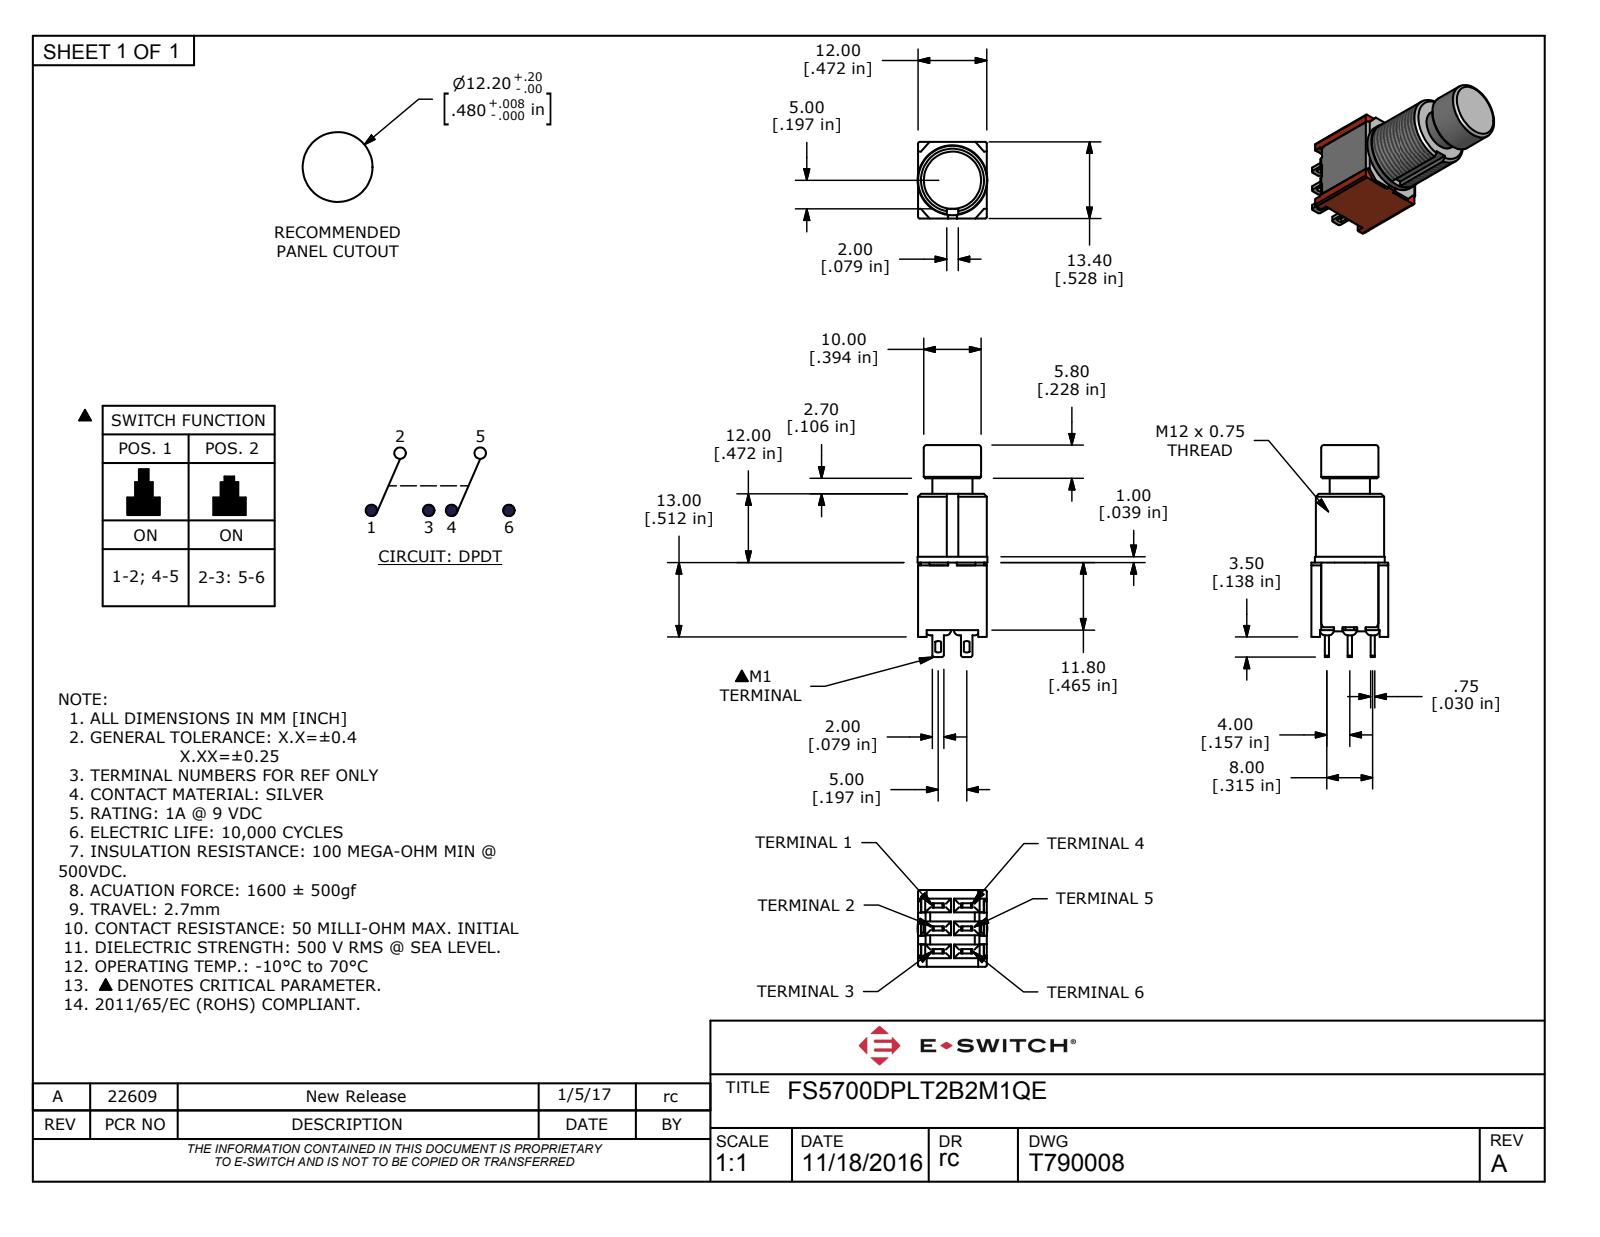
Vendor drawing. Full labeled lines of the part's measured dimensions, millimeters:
Part name (STEP PRODUCT): FS5700DPLT2B2M1QE
STEP written by: Autodesk Inventor 2022 (AUTOMOTIVE_DESIGN)
Units: millimetres
Bodies: 1 solid, 344 faces (258 planar, 83 cylindrical, 3 other)
Overall size (bounding box): 37 × 13.4 × 12.2
Volume: 2 139 mm³ · Surface area: 3 376 mm²
Round holes (diameter × count): ⌀9 ×1
Round bosses / shafts (diameter × count): ⌀12.2 ×1, ⌀12 ×1, ⌀10 ×1, ⌀7 ×1
Partial cylindrical surfaces — rounded edges, fillets, slot ends (radius × count): R0.2 ×26, R0.9 ×10, R0.3 ×4, R0.5 ×4, R0.1 ×2, R1 ×2
Main face-to-face distances: 1.2, 0.5, 11, 10.8, 10.3, 0.7, 11.5, 0.55, 11.45, 0.65
